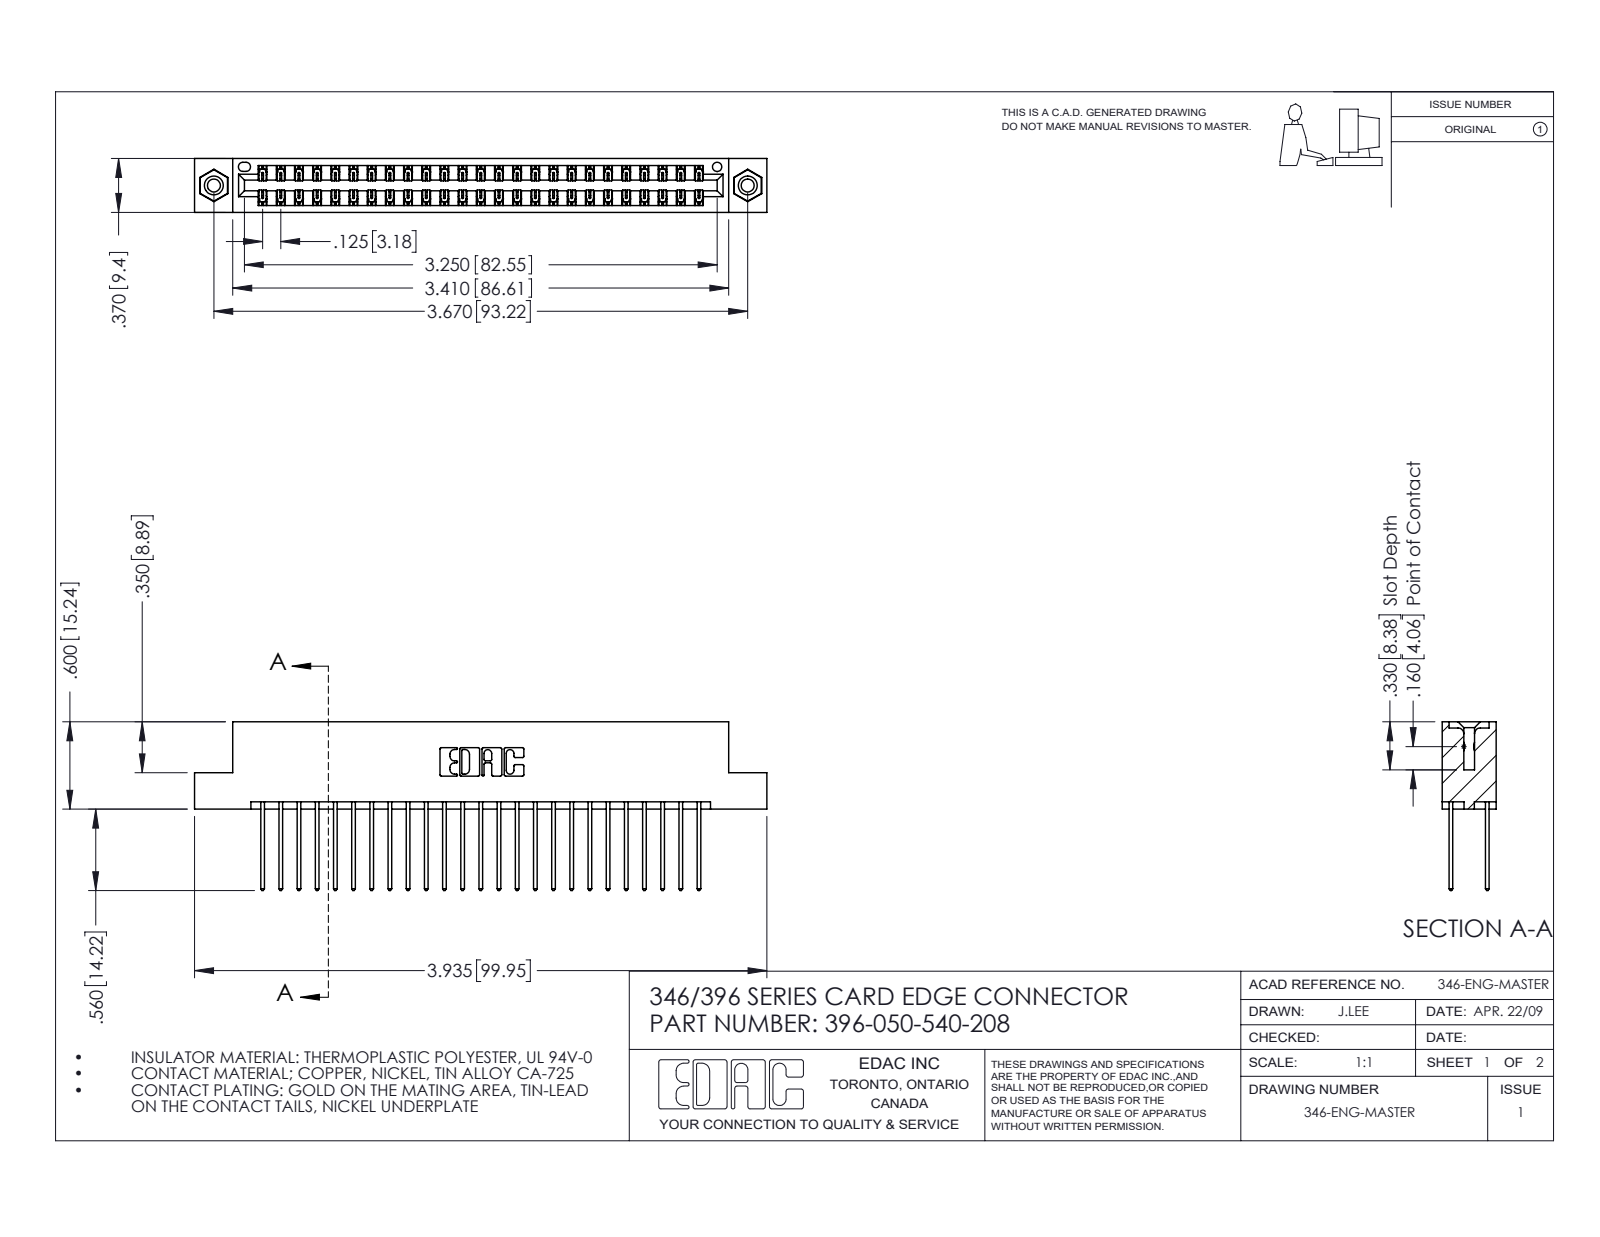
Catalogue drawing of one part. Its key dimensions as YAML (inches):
part_name: "345-250-001_345-250-003-102; 346 Part_Flush Mounting Lugs - 0.156 Dia-TI; 396-050-540-208; 345-292-001_345-293-140"
step_written_by: "SolidWorks 2016 (CONFIG_CONTROL_DESIGN)"
units: inches
bodies: {solids: 53, faces: 2782, planar: 1858, cylindrical: 908, other: 16}
overall_size: [3.935, 1.16, 0.37]
volume: 0.598
surface_area: 21.88
round_holes:
  - {diameter: 0.089, count: 2}
  - {diameter: 0.125, count: 2}
  - {diameter: 0.156, count: 2}
  - {diameter: 0.064, count: 1}
round_bosses_or_shafts:
  - {diameter: 0.155, count: 2}
partial_cylinders:
  - {radius: 0.006, count: 75}
  - {radius: 0.01, count: 50}
  - {radius: 0.01, count: 22}
  - {radius: 0.007, count: 6}
  - {radius: 0.031, count: 6}
  - {radius: 0.026, count: 3}
  - {radius: 0.014, count: 2}
  - {radius: 0.022, count: 2}
face_to_face_distances: [0.048, 0.322, 0.25, 0.072, 0.298, 0.025, 0.37, 0.275, 0.148, 0.222]
hole_center_spacings: [0.246, 3.462, 3.67]
